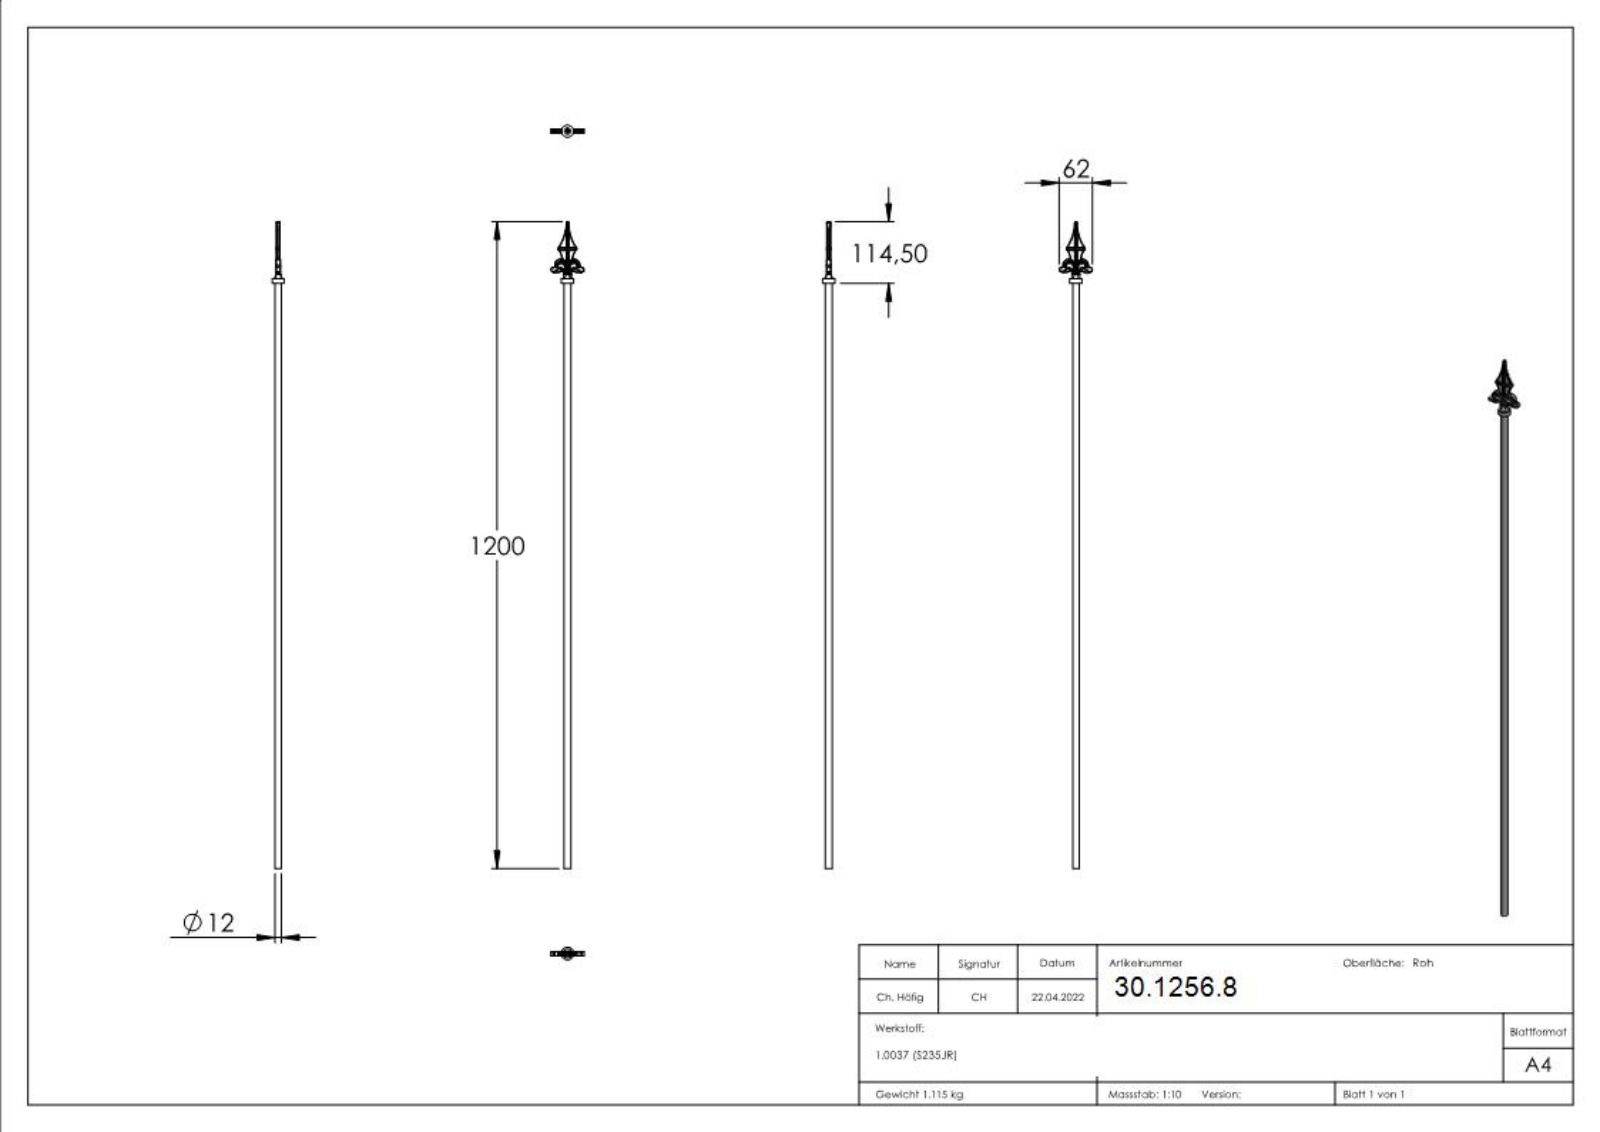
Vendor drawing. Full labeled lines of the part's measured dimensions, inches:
Part name (STEP PRODUCT): 18520
STEP written by: SolidWorks 2018 (CONFIG_CONTROL_DESIGN)
Units: inches
Bodies: 1 solid, 515 faces (159 planar, 89 cylindrical, 267 other)
Overall size (bounding box): 47.244 × 2.441 × 0.886
Volume: 8.733 in³ · Surface area: 76.69 in²
Round bosses / shafts (diameter × count): ⌀0.886 ×1, ⌀0.472 ×1
Partial cylindrical surfaces — rounded edges, fillets, slot ends (radius × count): R0.039 ×30, R0.02 ×15, R0.079 ×10, R0.157 ×2, R0.2 ×2, R0.394 ×2, R0.552 ×2, R0.553 ×2
Main face-to-face distances: 0.059, 0.256, 0.197, 0.315, 0.039, 0.02, 0.295, 0.236, 0.276, 0.335
